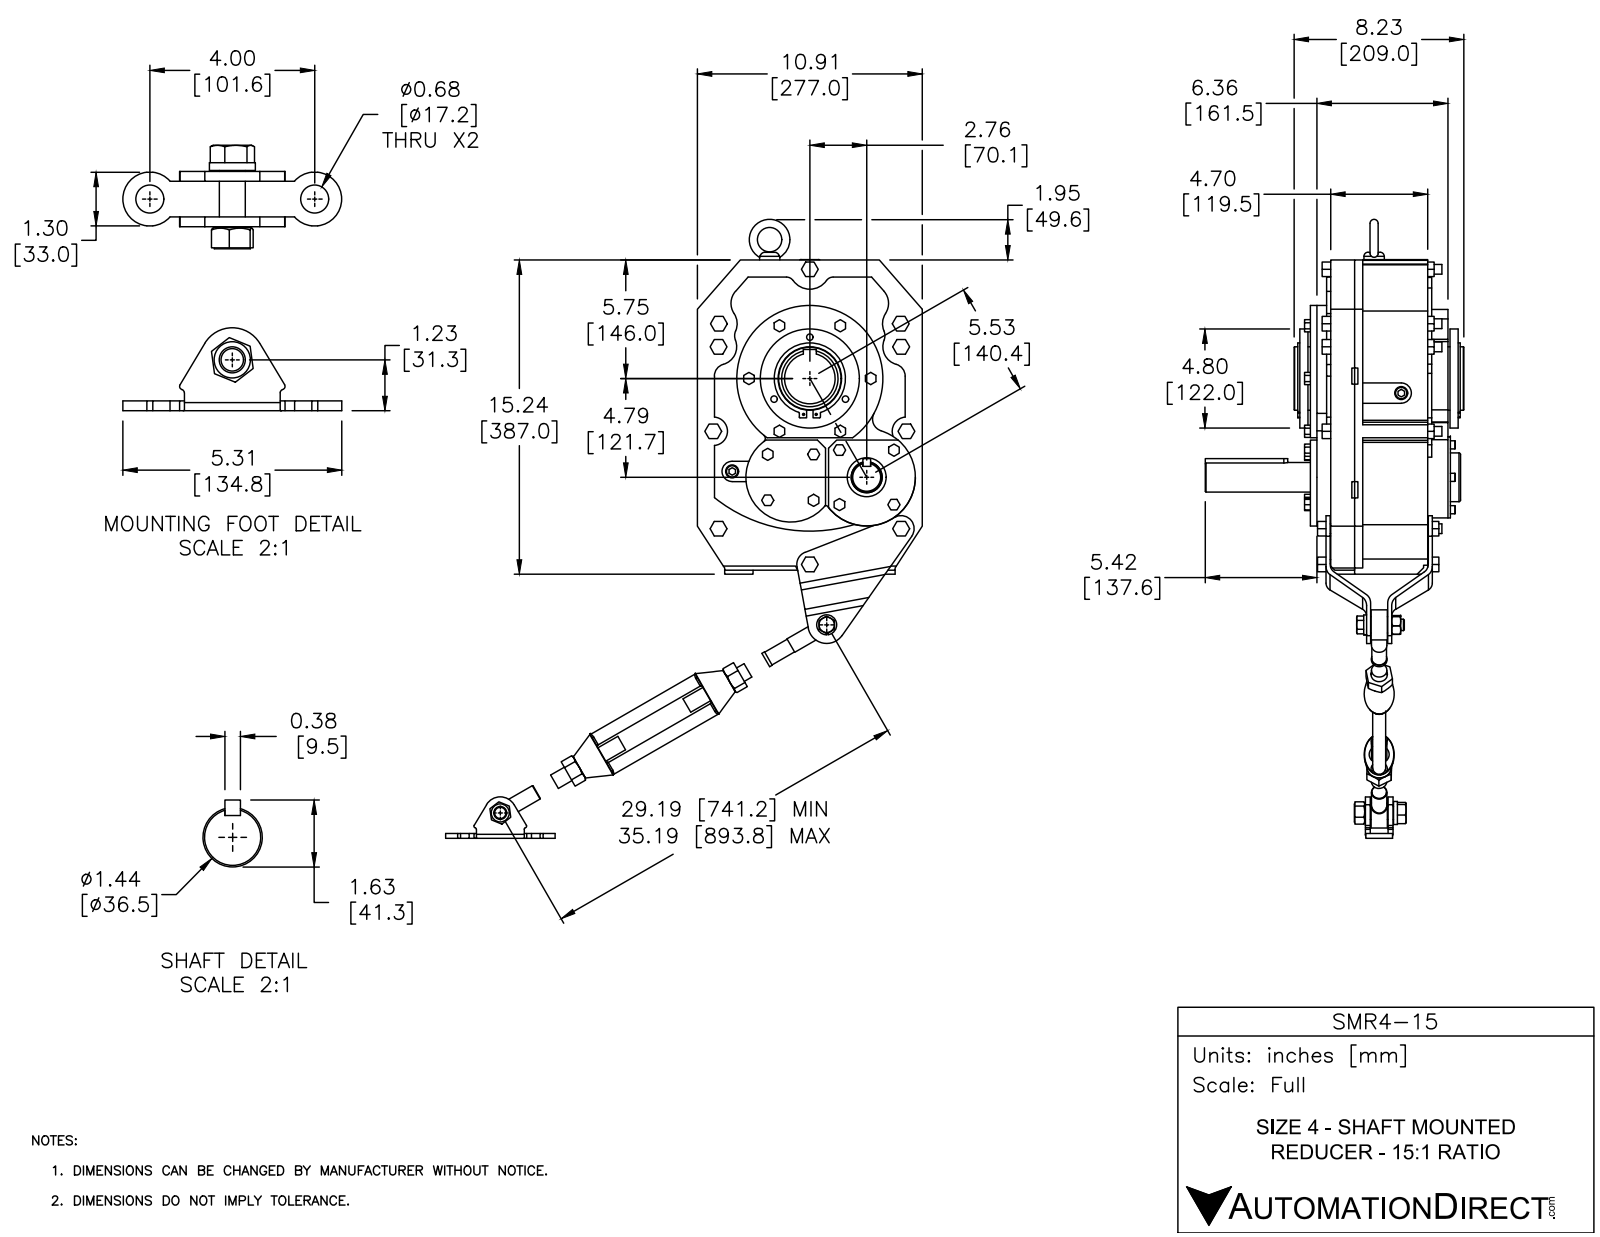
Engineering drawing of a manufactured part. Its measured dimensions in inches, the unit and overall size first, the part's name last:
Units: inches
Overall size (bounding box): 31.871 × 26.342 × 12.541
Round holes (diameter × count): ⌀0.512 ×10, ⌀0.63 ×6, ⌀0.422 ×4, ⌀0.531 ×4, ⌀0.313 ×3, ⌀0.098 ×2, ⌀0.677 ×2, ⌀0.689 ×2, ⌀0.787 ×2, ⌀0.551 ×1, ⌀0.559 ×1, ⌀0.571 ×1
Round bosses / shafts (diameter × count): ⌀0.472 ×10, ⌀0.75 ×4, ⌀0.394 ×4, ⌀1.457 ×2, ⌀0.711 ×2, ⌀0.63 ×2, ⌀7.087 ×1, ⌀4.803 ×1
Partial cylindrical surfaces — rounded edges, fillets, slot ends (radius × count): R0.118 ×17, R0.394 ×11, R0.492 ×6, R0.591 ×6, R0.689 ×6, R0.886 ×6, R0.039 ×4, R0.079 ×4
Main face-to-face distances: 0.197, 1.831, 0.984, 5.689, 0.236, 0.787, 6.358, 5.886, 4.902, 0.315
Hole centre spacings: 3.11, 4.398, 2, 8.819, 10.266, 1.122, 1.287, 1.609
Volume: 853 in³ · Surface area: 1 914 in²
Bodies: 74 solids, 1270 faces (715 planar, 430 cylindrical, 125 other)
Part name (STEP PRODUCT): SMR4-15; SMR4-TA; SMR4-TA_5; SMR4-TA_4 (+4 more)
STEP written by: SolidWorks 2016 (AUTOMOTIVE_DESIGN)
